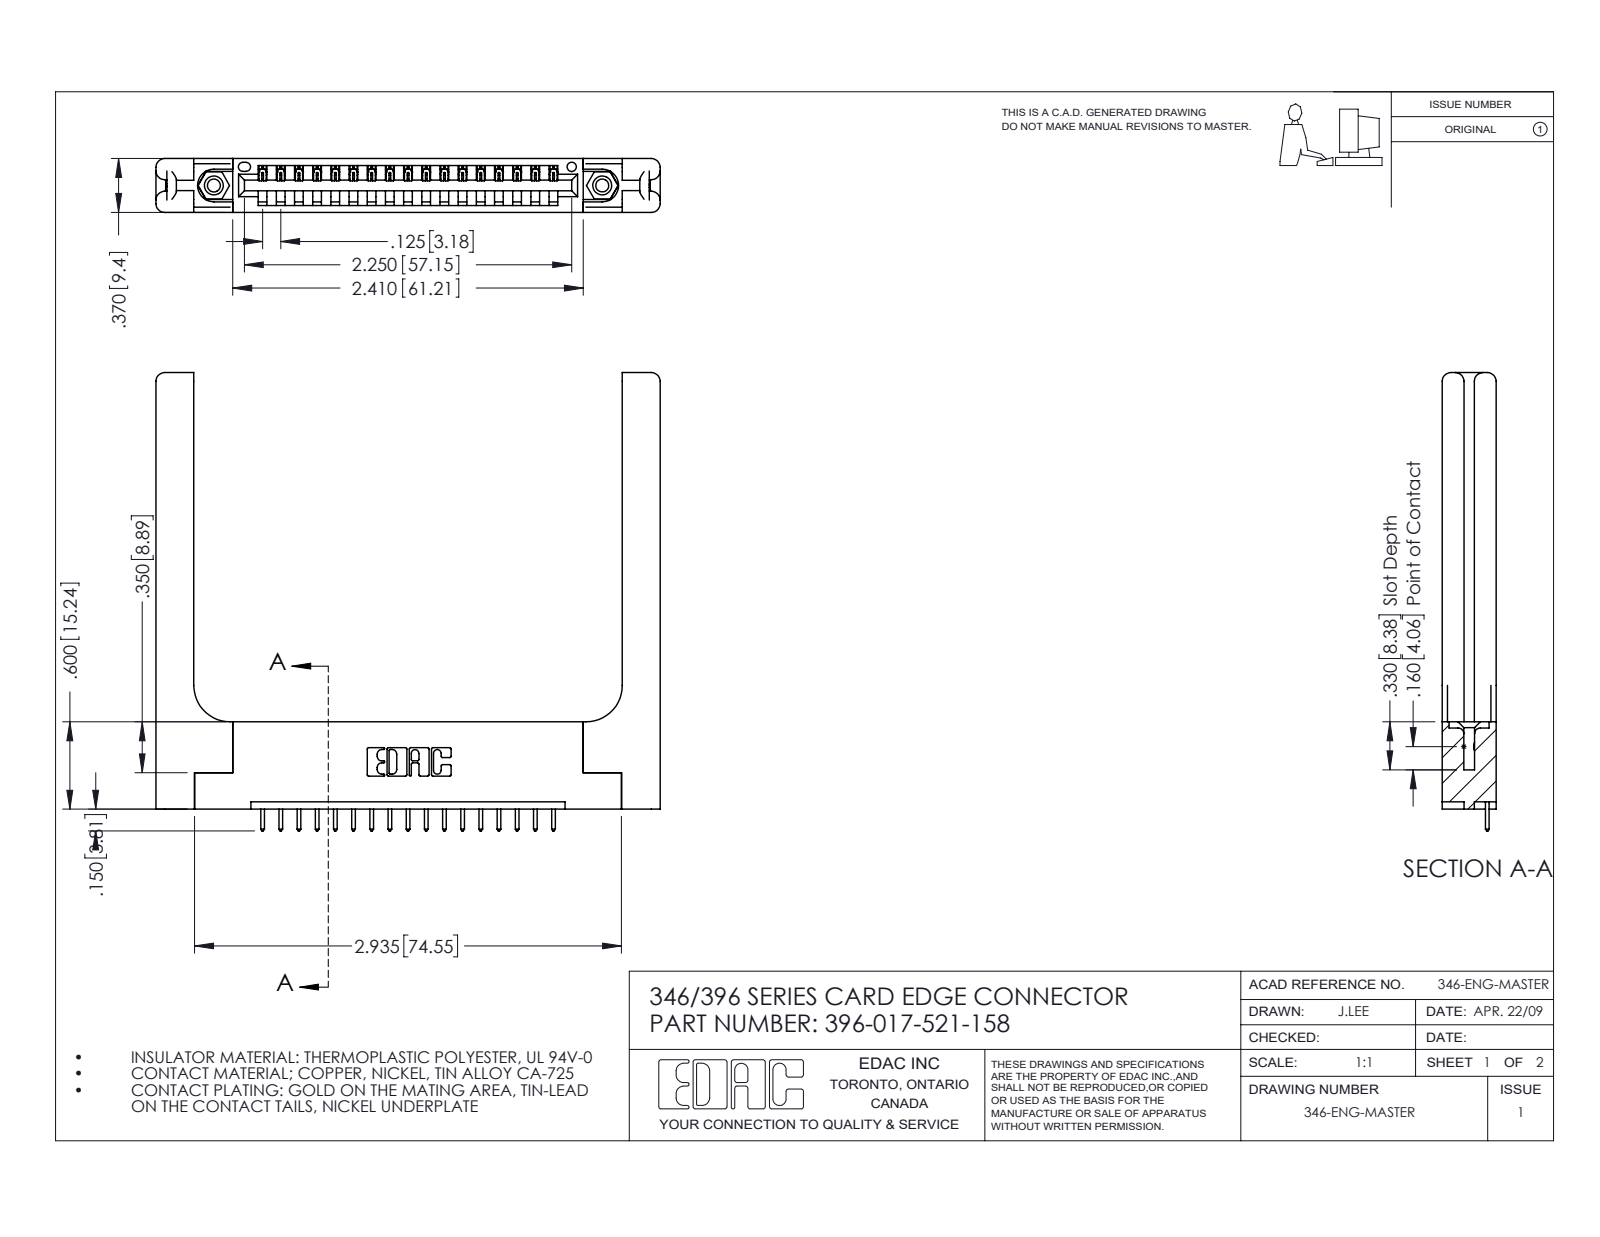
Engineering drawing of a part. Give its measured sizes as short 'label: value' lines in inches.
name: 346 Part_Flush Mounting Lugs - 0.156 Dia-TH; 346-220-058_345-220-058; 396-017-521-158; 345-292-001_345-293-121 (+1 more)
written by: SolidWorks 2016 (CONFIG_CONTROL_DESIGN)
unit: in
bodies: 22 solids, 1364 faces (904 planar, 400 cylindrical, 60 other)
size: 3.466 × 3.15 × 0.37
volume: 0.96 in³; area: 23.19 in²
holes: 2× ⌀0.089, 2× ⌀0.125, 2× ⌀0.156, 1× ⌀0.064
bosses: 2× ⌀0.155
rounds: 34× R0.006, 34× R0.01, 22× R0.01, 16× R0.06, 6× R0.007, 6× R0.031, 3× R0.026, 2× R0.03
face distances: 0.37, 0.15, 0.072, 0.148, 0.048, 0.322, 0.25, 0.102, 0.22, 0.173
hole spacings: 0.246, 2.463, 2.67
